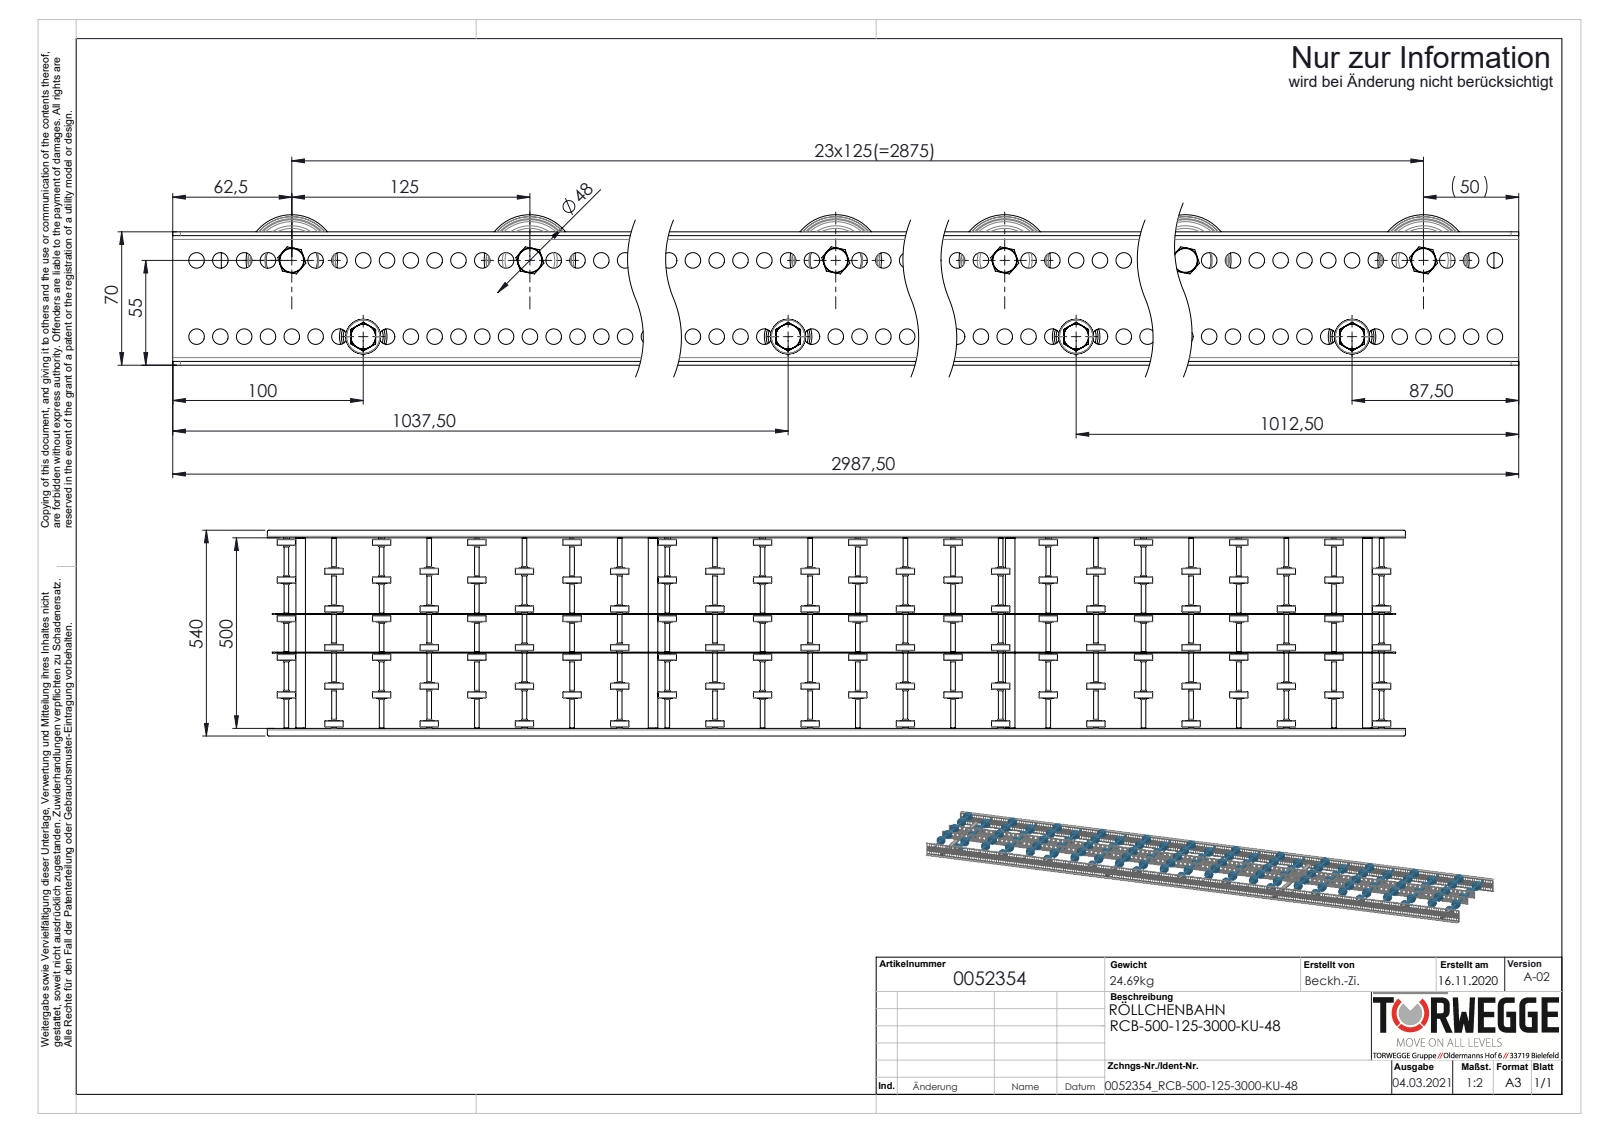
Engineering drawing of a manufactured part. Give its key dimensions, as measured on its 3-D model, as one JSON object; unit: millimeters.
{"part_name": "0011532_2300-48-8; 0052354; Profil_LRB-20x70x20x2_KFG_S109080_U-PROFIL-20-70-20-2-LRB-L=2987,5; Röllchenachse-für-Konfiguration_EL500 (+6 more)", "step_written_by": "SolidWorks 2020 (AUTOMOTIVE_DESIGN)", "units": "millimeters", "bodies": {"solids": 336, "faces": 13440, "planar": 2208, "cylindrical": 5360, "other": 5872}, "overall_size": [2987.5, 540, 79], "volume_mm3": 5383000, "surface_area_mm2": 4168000, "round_holes": [[8.2, 476], [8.5, 118], [6.65, 24], [9.65, 24], [13.7, 24], [6.8, 4], [21, 4]], "round_bosses_or_shafts": [[8, 28], [48, 24], [27, 24], [12.7, 24], [12.5, 24], [12, 24], [25, 4]], "partial_cylinders_radius": [[4, 8], [2, 4], [5, 4]], "face_to_face_distances": [2, 502, 101.3, 2.5, 68, 500, 504, 200.1, 301.4, 98.8], "hole_center_spacings": [12.5, 25, 37.5, 50, 62.5, 75, 87.5, 100]}
